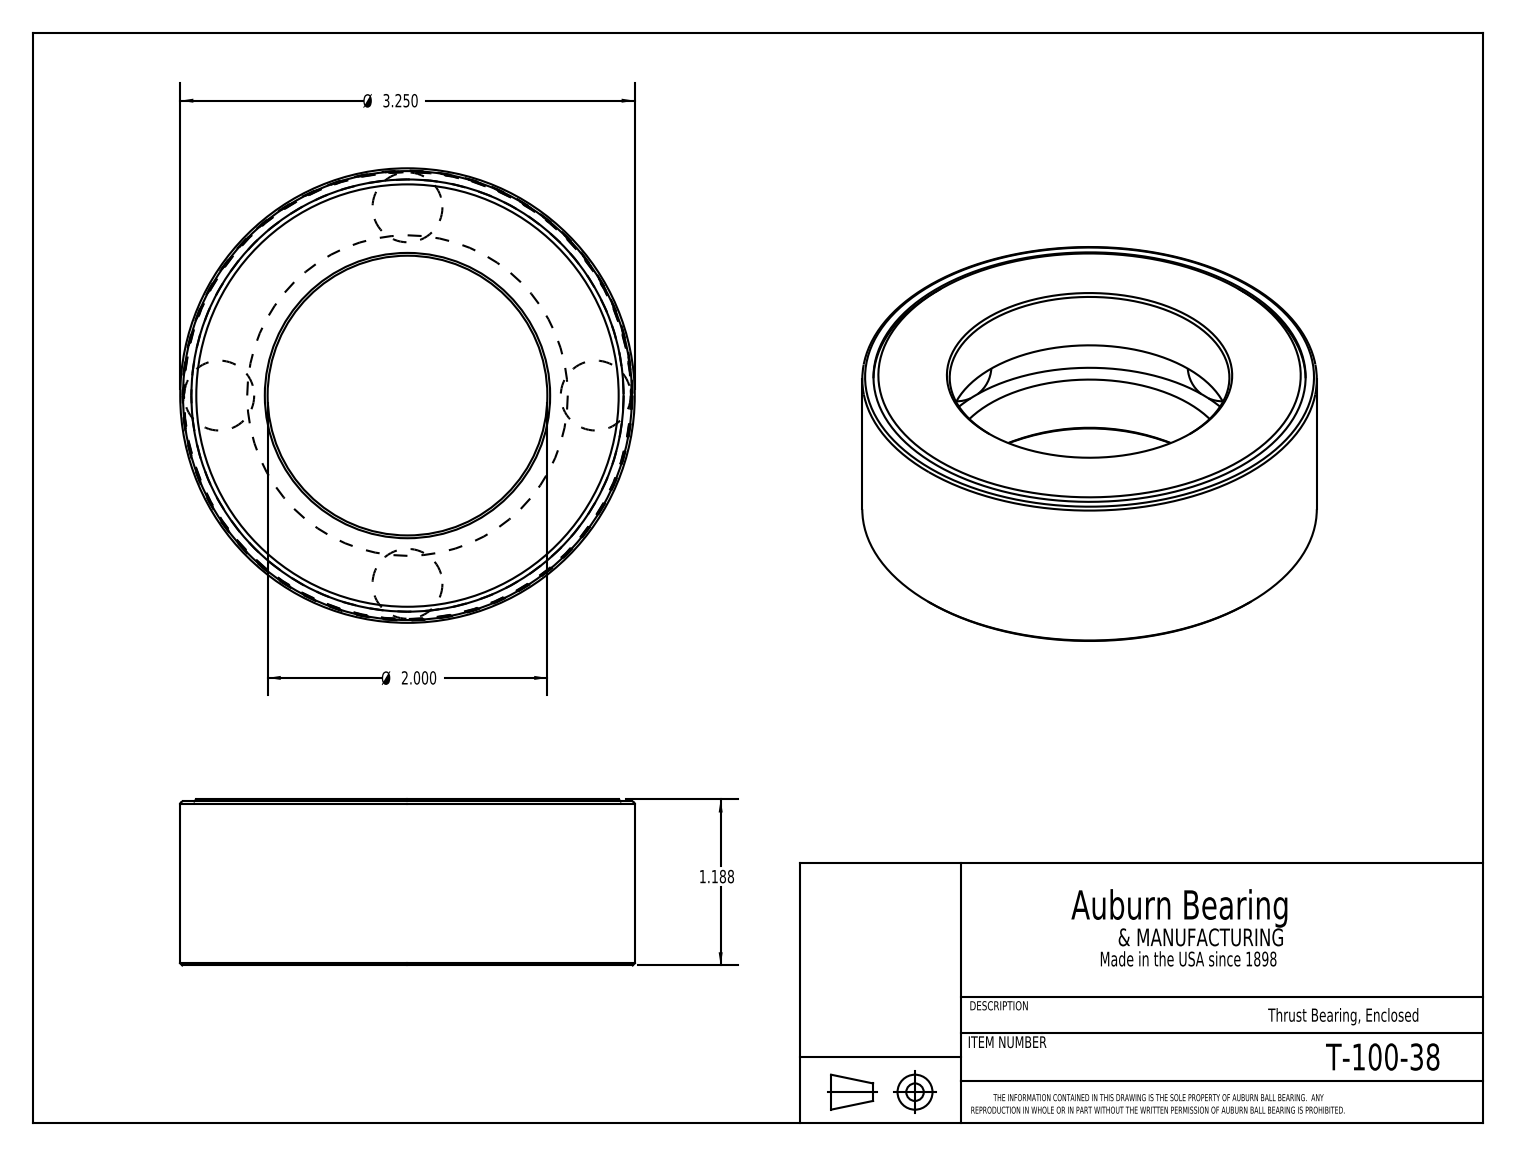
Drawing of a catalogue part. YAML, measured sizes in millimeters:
part_name: "T-100-38"
step_written_by: "SolidWorks 2016 (CONFIG_CONTROL_DESIGN)"
units: millimeters
bodies: {solids: 6, faces: 28, planar: 9, cylindrical: 7, other: 12}
overall_size: [82.6, 82.6, 30.2]
volume: 71430
surface_area: 34860
round_holes:
  - {diameter: 50.8, count: 1}
  - {diameter: 78.5, count: 1}
  - {diameter: 81.5, count: 1}
round_bosses_or_shafts:
  - {diameter: 82.6, count: 1}
  - {diameter: 81.2, count: 1}
face_to_face_distances: [30.1, 11.3, 18.9, 7.6, 29.8, 18.5, 10.9, 0.4, 29.3, 18]
